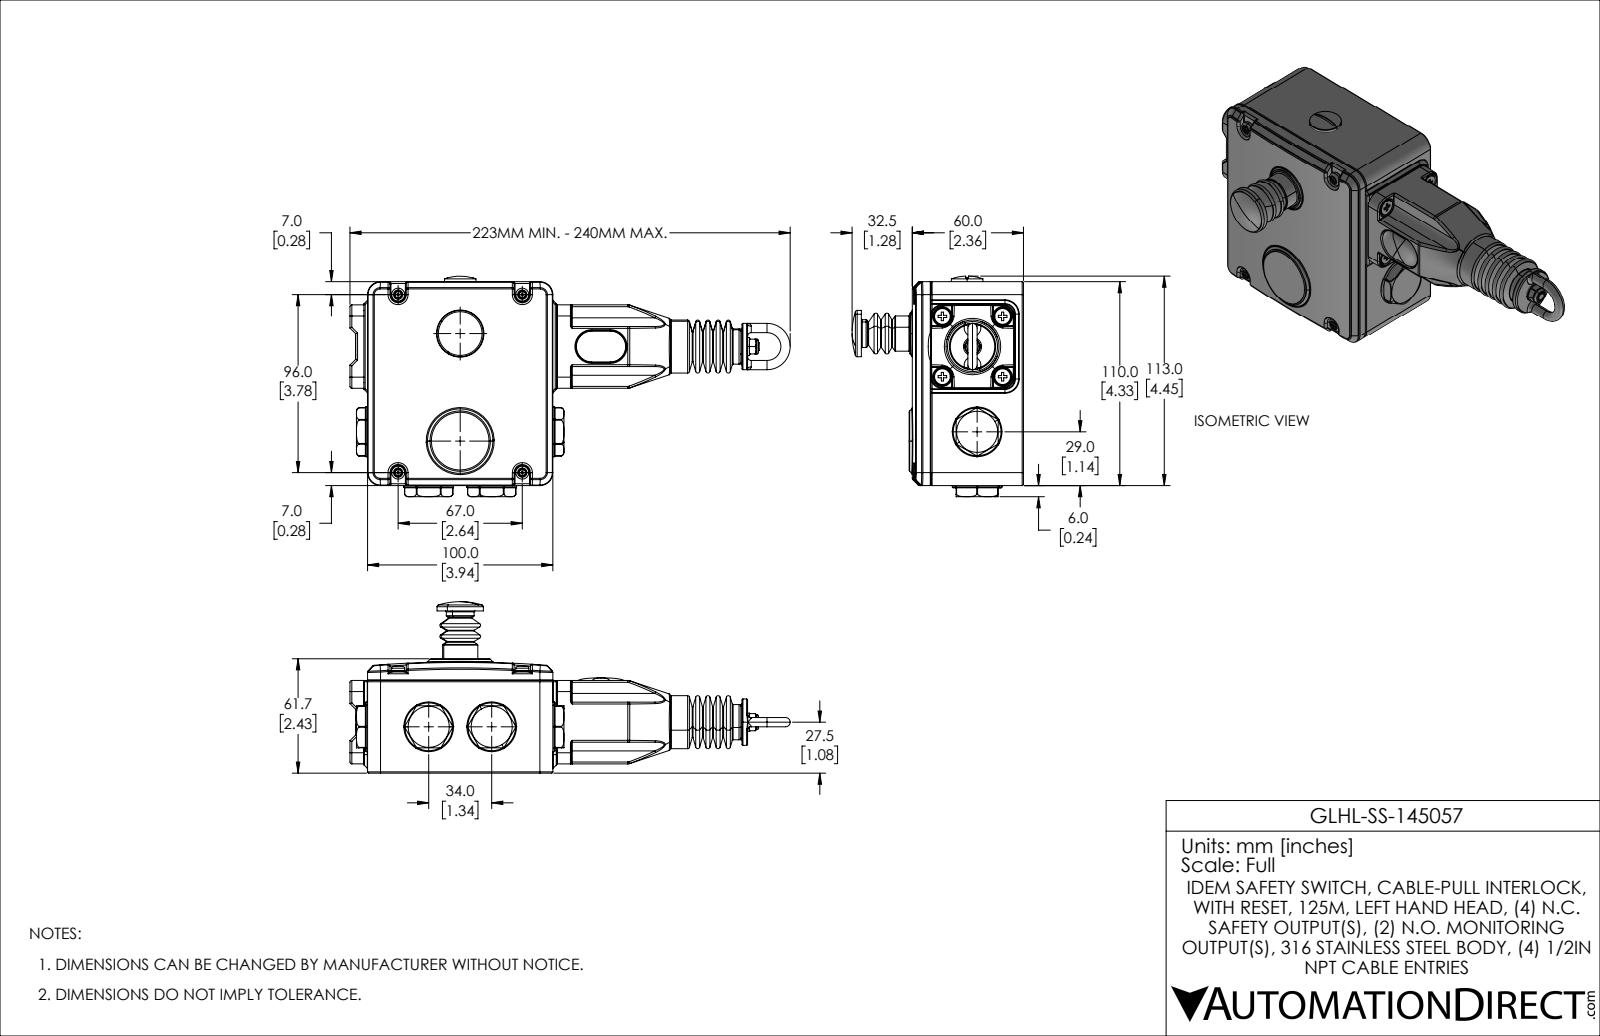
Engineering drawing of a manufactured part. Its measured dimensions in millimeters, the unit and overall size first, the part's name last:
Units: millimetres
Overall size (bounding box): 238.1 × 116.7 × 92.8
Round holes (diameter × count): ⌀5 ×9, ⌀5.3 ×9, ⌀9.6 ×8, ⌀9 ×5, ⌀3.3 ×4, ⌀4 ×4, ⌀4.1 ×4, ⌀4.8 ×4, ⌀5.4 ×4, ⌀5.8 ×4, ⌀3 ×3, ⌀4.4 ×3
Round bosses / shafts (diameter × count): ⌀5 ×11, ⌀8.5 ×8, ⌀4.4 ×8, ⌀7 ×5, ⌀3.5 ×4, ⌀1.3 ×4, ⌀24 ×3, ⌀23.8 ×3
Partial cylindrical surfaces — rounded edges, fillets, slot ends (radius × count): R0.5 ×206, R1 ×159, R0.2 ×64, R0.7 ×48, R0.2 ×14, R0.3 ×12, R0.1 ×8, R0.8 ×8
Main face-to-face distances: 1, 3.5, 55.4, 2, 2.9, 52.5, 102, 4, 110, 8.5
Hole centre spacings: 32.5, 32.5, 23, 9.5, 22.9, 23, 23, 32.5
Volume: 288 700 mm³ · Surface area: 168 300 mm²
Bodies: 34 solids, 3522 faces (955 planar, 1160 cylindrical, 1407 other)
Part name (STEP PRODUCT): GLHL-SS-145057
STEP written by: SolidWorks 2021 (AUTOMOTIVE_DESIGN)
